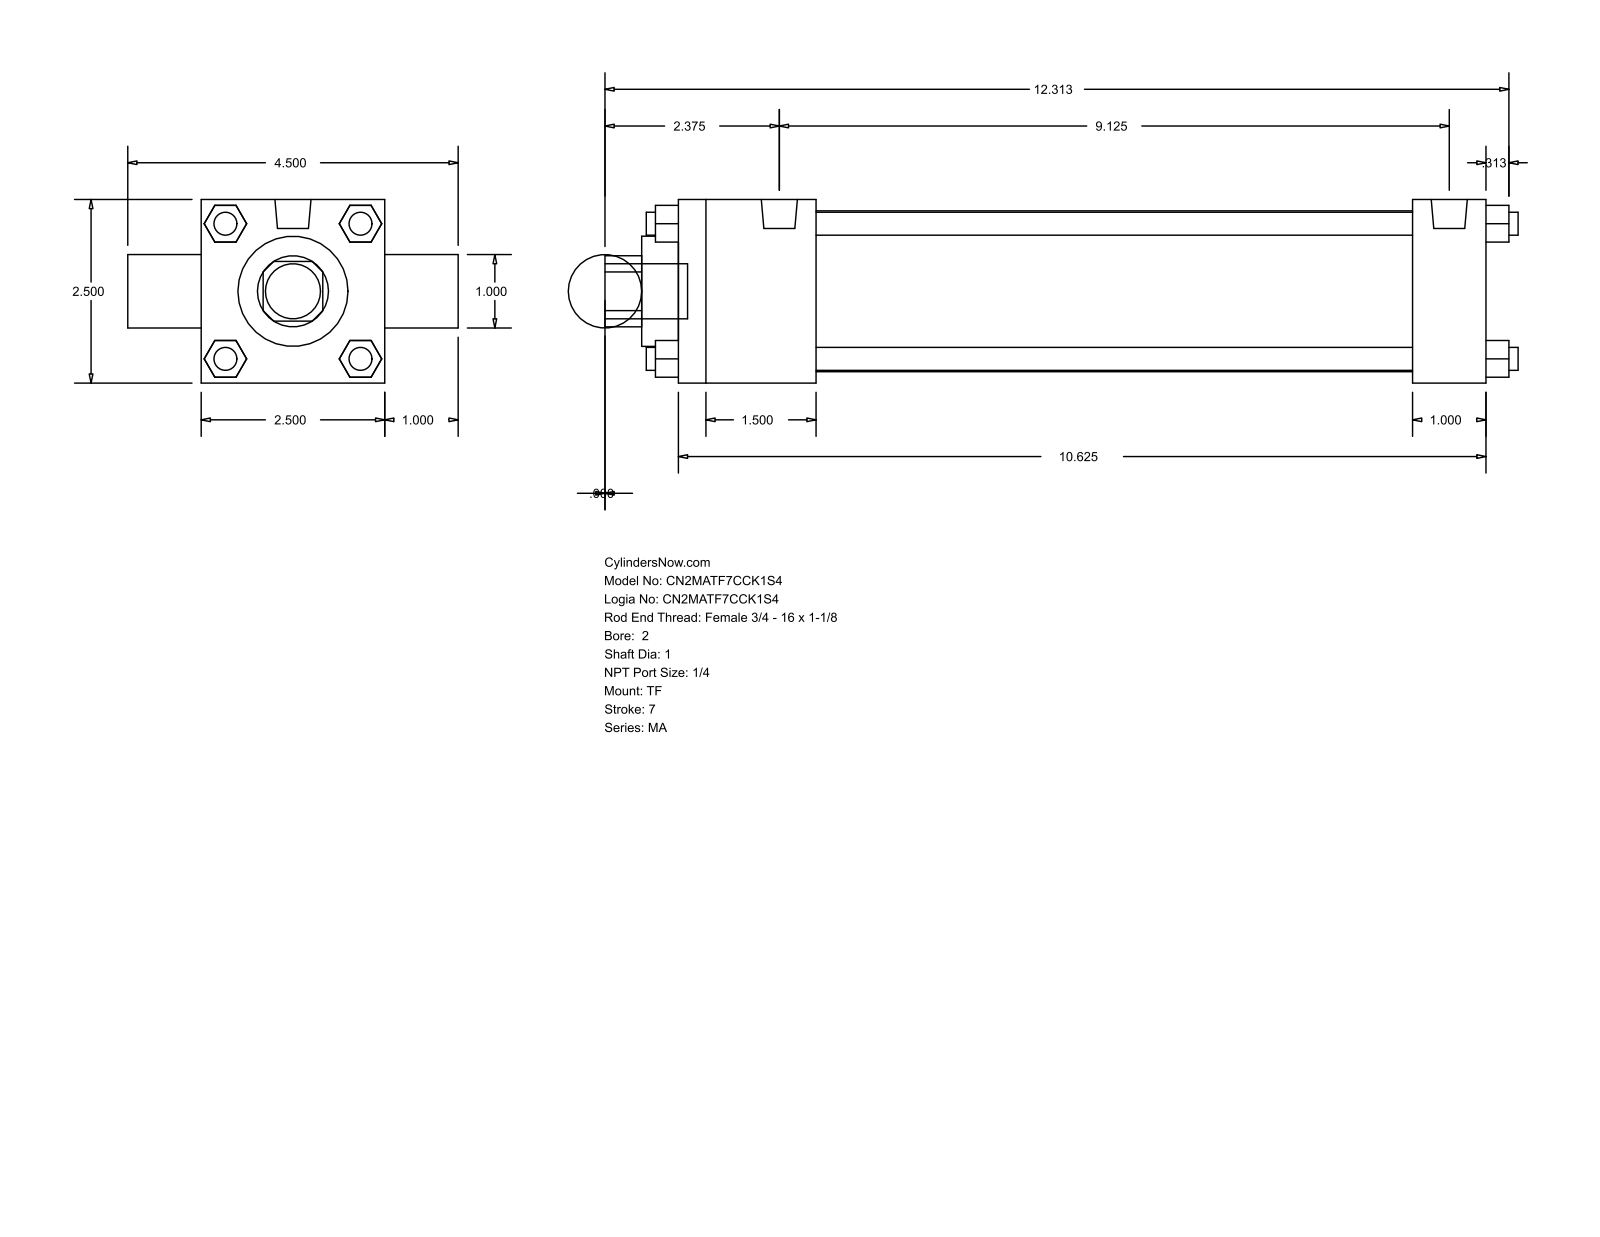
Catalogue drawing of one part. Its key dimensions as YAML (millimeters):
part_name: "MA_TF__0200_1"
step_written_by: "GSSL Pune (CONFIG_CONTROL_DESIGN)"
units: millimeters
bodies: {solids: 0, faces: 120, planar: 92, cylindrical: 28, other: 0}
overall_size: [315.91, 114.3, 63.5]
round_holes:
  - {diameter: 25.4, count: 2}
  - {diameter: 38.1, count: 1}
  - {diameter: 55.63, count: 1}
round_bosses_or_shafts:
  - {diameter: 7.94, count: 7}
  - {diameter: 12.49, count: 2}
  - {diameter: 19.05, count: 1}
partial_cylinders:
  - {radius: 12.29, count: 1}
face_to_face_distances: [63.5, 25.4, 279.4, 12.7, 47.63, 254, 206.37, 231.77, 88.9, 40.47]
